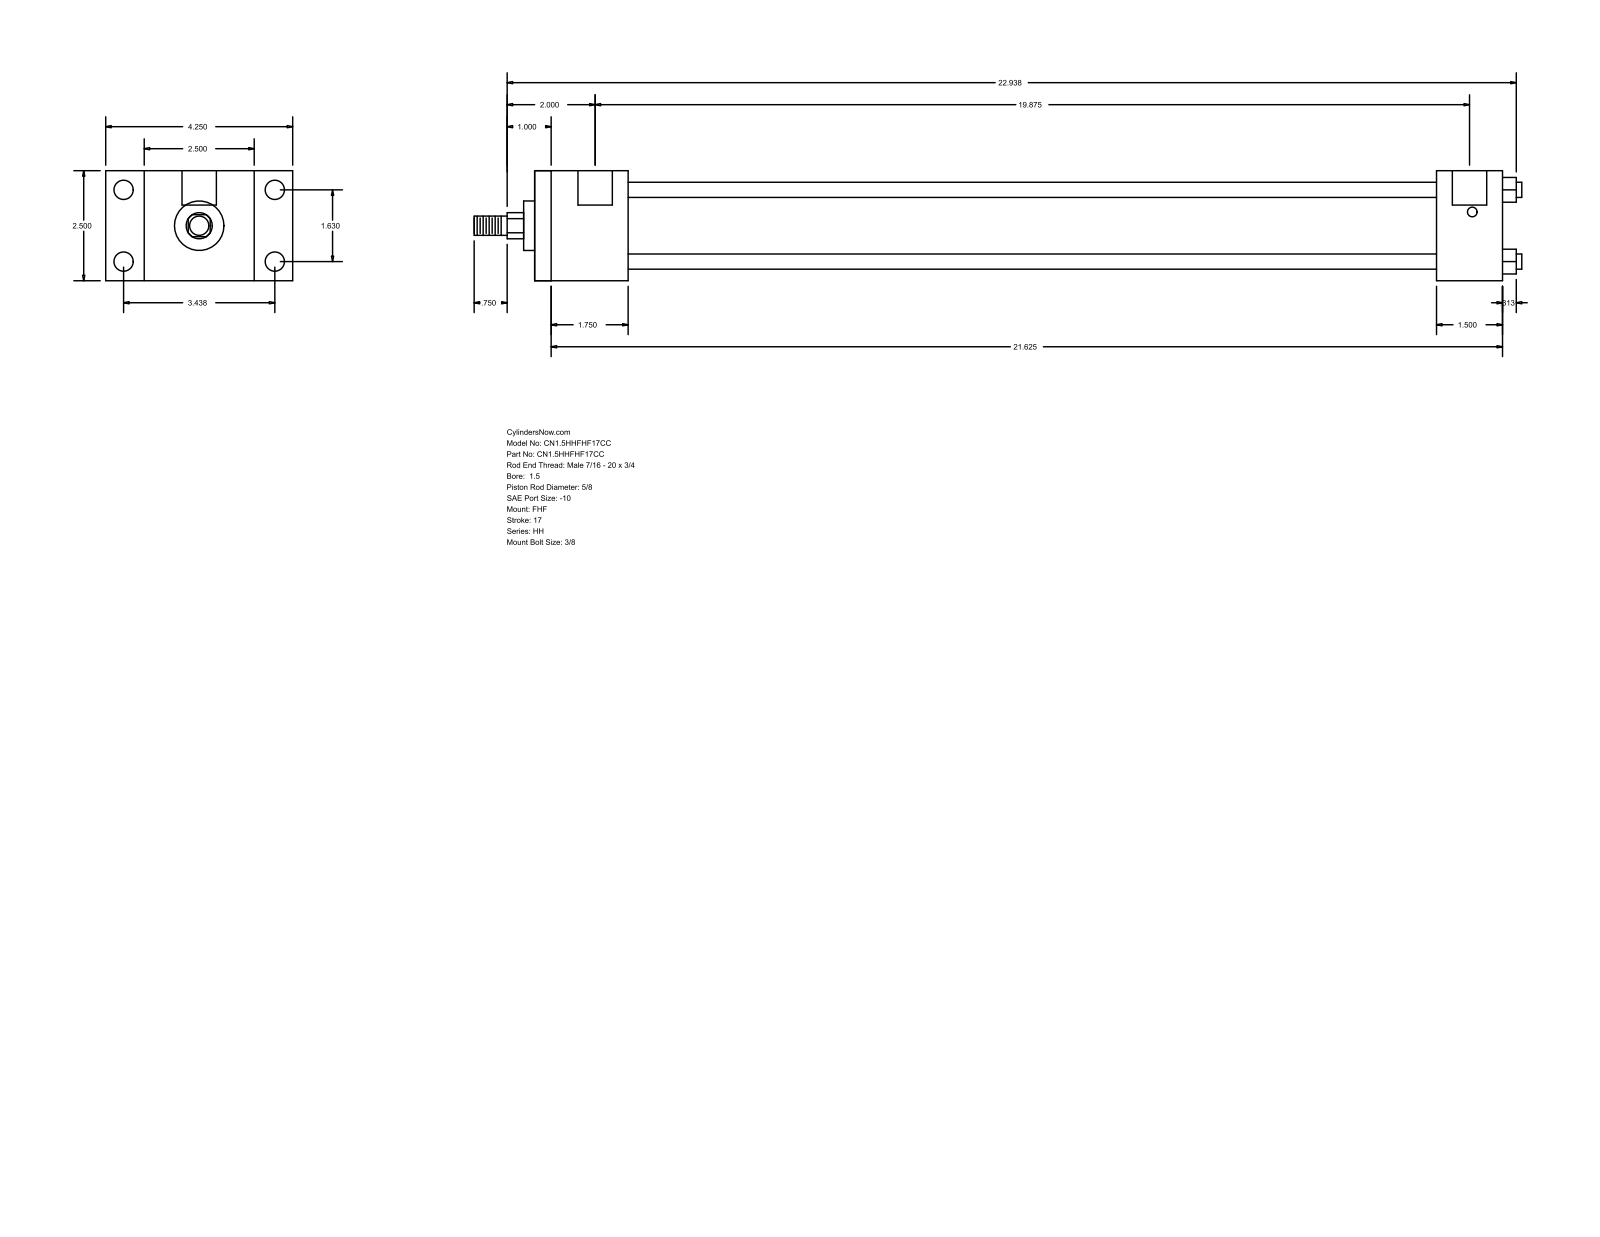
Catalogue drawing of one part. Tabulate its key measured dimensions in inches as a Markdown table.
| quantity | value |
| --- | --- |
| part name | HH_FHF__0150_0.625 |
| STEP written by | GSSL Pune (CONFIG_CONTROL_DESIGN) |
| units | inches |
| bodies | 0 solids, 88 faces (60 planar, 28 cylindrical, 0 other) |
| overall size | 23.813 × 4.25 × 2.5 |
| round holes (diameter × count) | 0.219 × 4, 0.438 × 4, 0.781 × 2 |
| round bosses / shafts (diameter × count) | 0.345 × 4, 1.75 × 1, 1.125 × 1, 0.625 × 1, 0.437 × 1 |
| partial cylindrical surfaces (radius × count) | 0.297 × 1 |
| main face-to-face distances | 2.5, 0.875, 3.375, 2.125, 4.25, 22, 19.875, 20.5, 18.375, 1.5 |
| hole center spacings | 0.063, 1.63, 3.438, 3.805, 19.937, 20, 19.875 |
